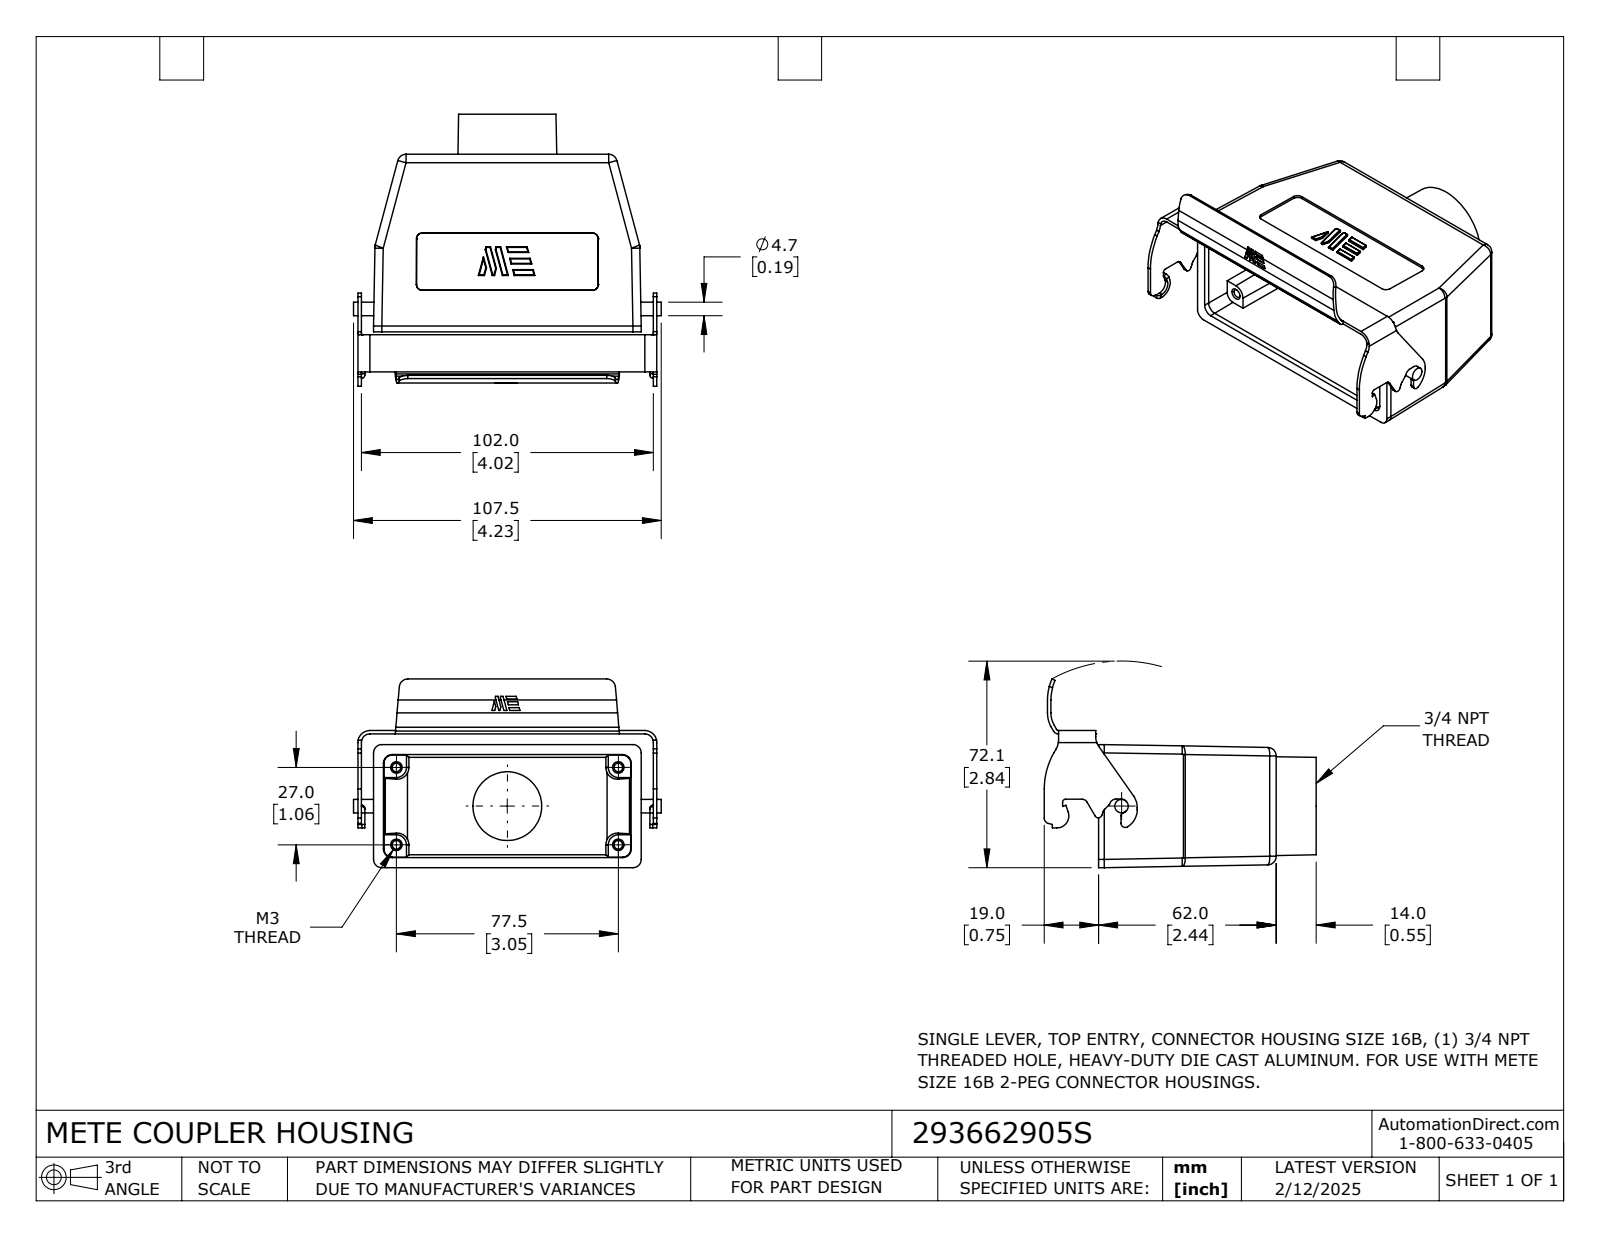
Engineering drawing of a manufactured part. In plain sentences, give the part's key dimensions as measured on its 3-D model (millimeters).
The part is named "293662905S". Its 3-D file was written by "SolidWorks 2024 (CONFIG_CONTROL_DESIGN)". It is 1 solid with 389 faces: 205 planar, 150 cylindrical and 34 other. Overall it measures 107.5 by 95 by 65.9 millimeters. Its volume is 74 318 cubic millimeters and its surface area 47 770 square millimeters. Round holes: 4 of diameter 3, 1 of diameter 24, 1 of diameter 27. Round bosses or shafts: 1 of diameter 4.7. Partial cylindrical surfaces (rounded edges, fillets, slot ends): 35 of radius 0.2, 13 of radius 3, 11 of radius 2, 6 of radius 1, 6 of radius 2.9, 5 of radius 2.5, 3 of radius 4.2, 2 of radius 6. The main face-to-face distances are 3.5, 1.2, 2.71, 0.79, 3, 103.2, 7.85, 11.35, 59, 62. The hole center spacings are 41.03, 27, 77.5, 82.07.
